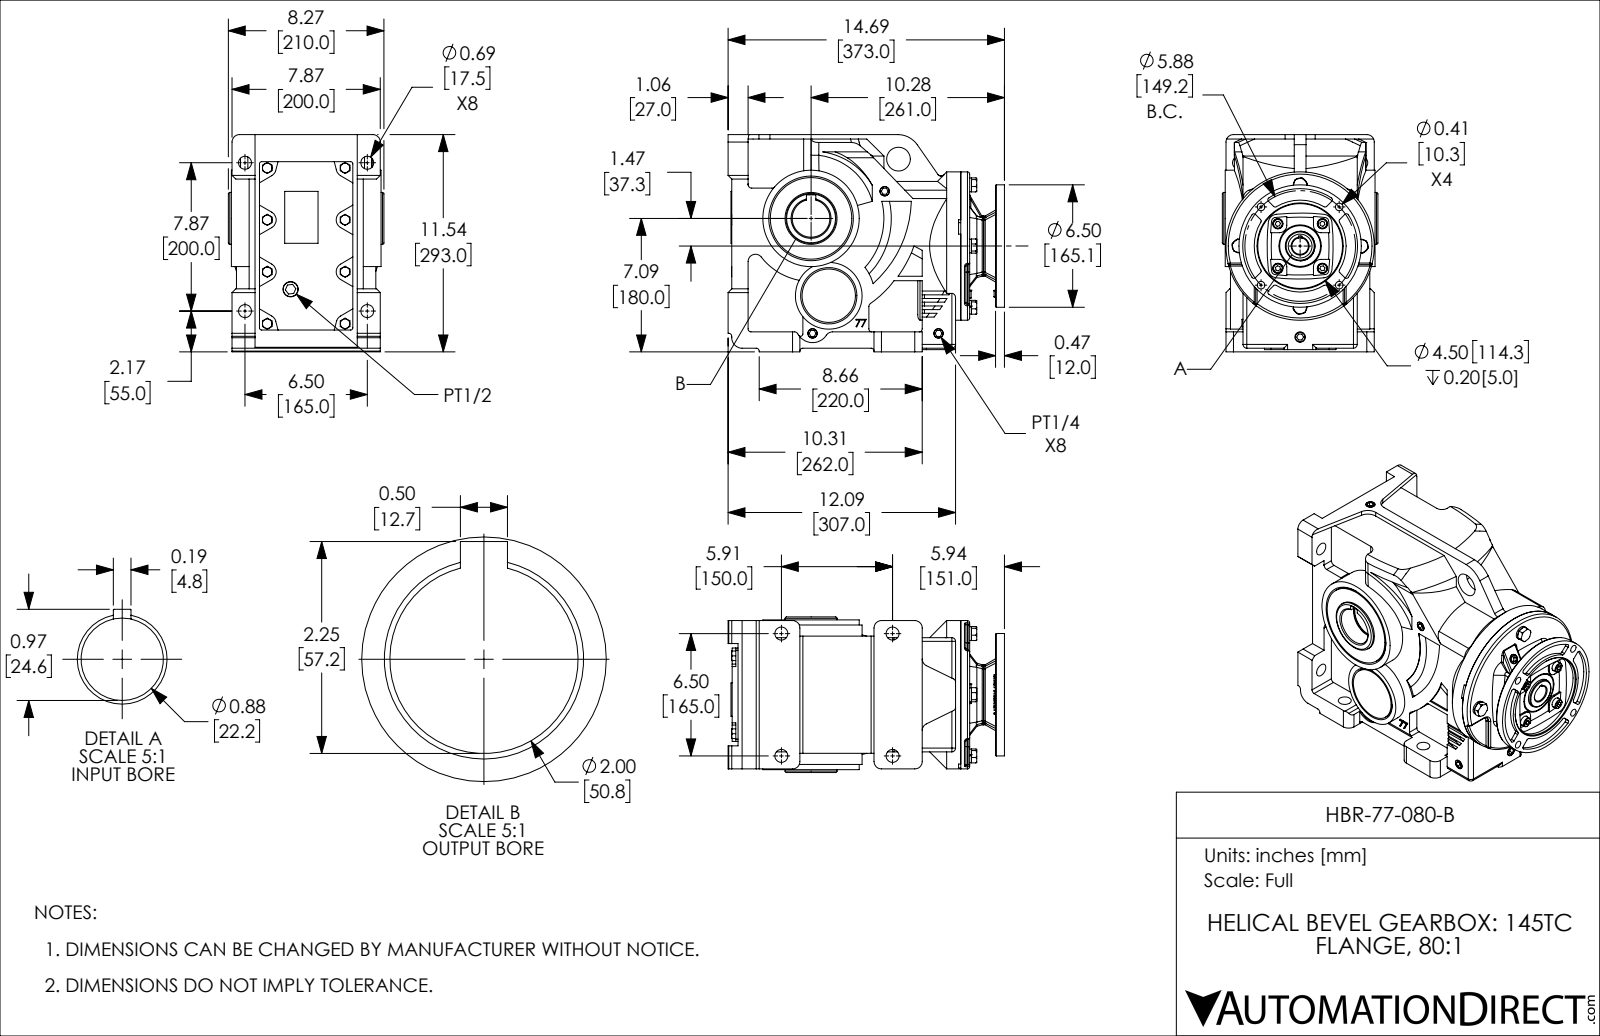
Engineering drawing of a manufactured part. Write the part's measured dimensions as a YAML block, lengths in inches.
part_name: "HBR-77-080-B"
step_written_by: "SolidWorks 2018 (AUTOMOTIVE_DESIGN)"
units: inches
bodies: {solids: 44, faces: 2018, planar: 886, cylindrical: 704, other: 428}
overall_size: [14.685, 11.535, 8.268]
volume: 321
surface_area: 1848
round_holes:
  - {diameter: 0.268, count: 12}
  - {diameter: 0.354, count: 12}
  - {diameter: 0.689, count: 8}
  - {diameter: 0.315, count: 4}
  - {diameter: 0.335, count: 4}
  - {diameter: 0.402, count: 4}
  - {diameter: 0.406, count: 4}
  - {diameter: 0.433, count: 4}
  - {diameter: 0.551, count: 4}
  - {diameter: 0.438, count: 3}
  - {diameter: 0.118, count: 2}
  - {diameter: 0.487, count: 2}
round_bosses_or_shafts:
  - {diameter: 0.315, count: 8}
  - {diameter: 0.724, count: 4}
  - {diameter: 0.512, count: 4}
  - {diameter: 0.394, count: 4}
  - {diameter: 7.874, count: 1}
  - {diameter: 6.5, count: 1}
  - {diameter: 5.118, count: 1}
  - {diameter: 3.543, count: 1}
partial_cylinders:
  - {radius: 0.394, count: 40}
  - {radius: 0.177, count: 24}
  - {radius: 0.118, count: 23}
  - {radius: 0.197, count: 12}
  - {radius: 0.315, count: 12}
  - {radius: 0.079, count: 11}
  - {radius: 0.157, count: 11}
  - {radius: 0.472, count: 10}
face_to_face_distances: [0.236, 0.472, 0.315, 4.961, 0.276, 0.787, 0.512, 5.748, 0.551, 5.276]
hole_center_spacings: [2.384, 5.716, 2.38, 2.756, 4.968, 6.496, 1.673, 2.937]
